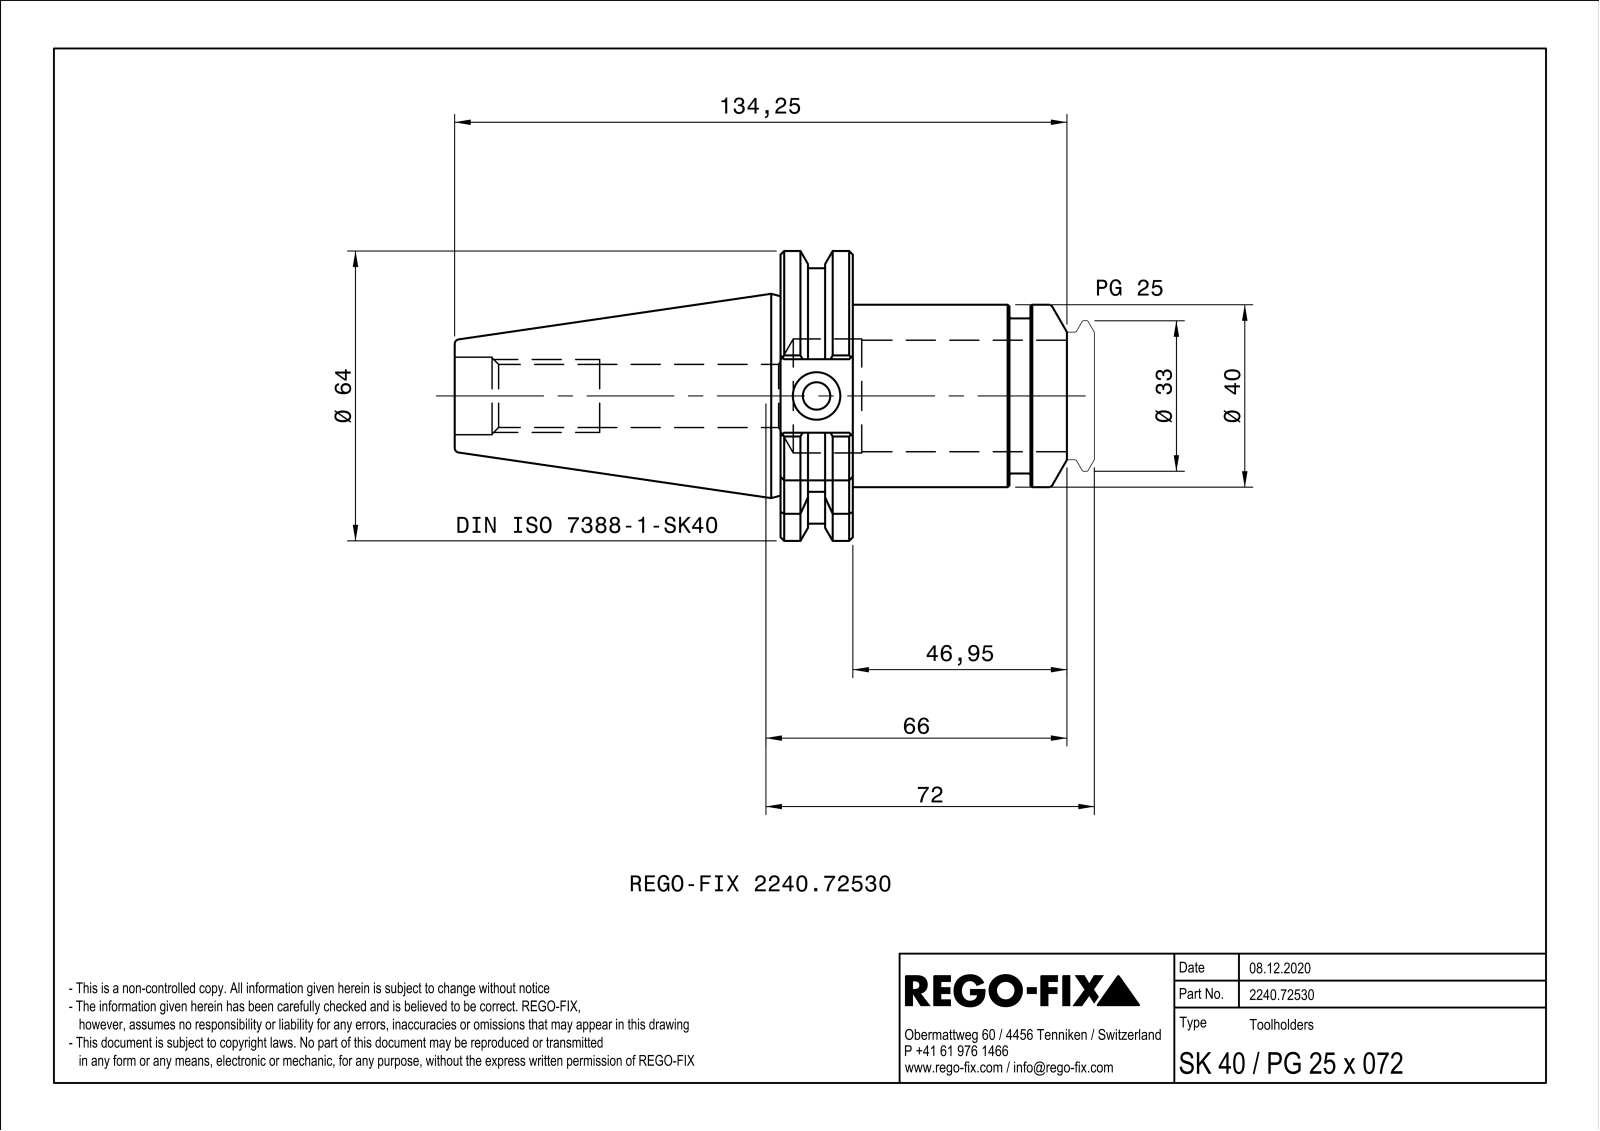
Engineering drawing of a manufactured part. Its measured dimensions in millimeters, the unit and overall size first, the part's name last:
Units: millimetres
Overall size (bounding box): 134.25 × 63.55 × 61.01
Round holes (diameter × count): ⌀3.5 ×5, ⌀6 ×1, ⌀10 ×1, ⌀13.84 ×1, ⌀17 ×1, ⌀25 ×1
Round bosses / shafts (diameter × count): ⌀40 ×1, ⌀34 ×1
Partial cylindrical surfaces — rounded edges, fillets, slot ends (radius × count): R0.5 ×13, R28 ×1, R31.77 ×1
Main face-to-face distances: 15.85, 34.35, 50.2, 4.6, 38.95, 54.8, 47.3, 16.1, 126.25, 121.65
Volume: 127 573 mm³ · Surface area: 30 673 mm²
Bodies: 1 solid, 128 faces (43 planar, 41 cylindrical, 44 other)
Part name (STEP PRODUCT): NOCUT
STEP written by: SIEMENS PLM Software Solid Edge ST10 (AUTOMOTIVE_DESIGN)
